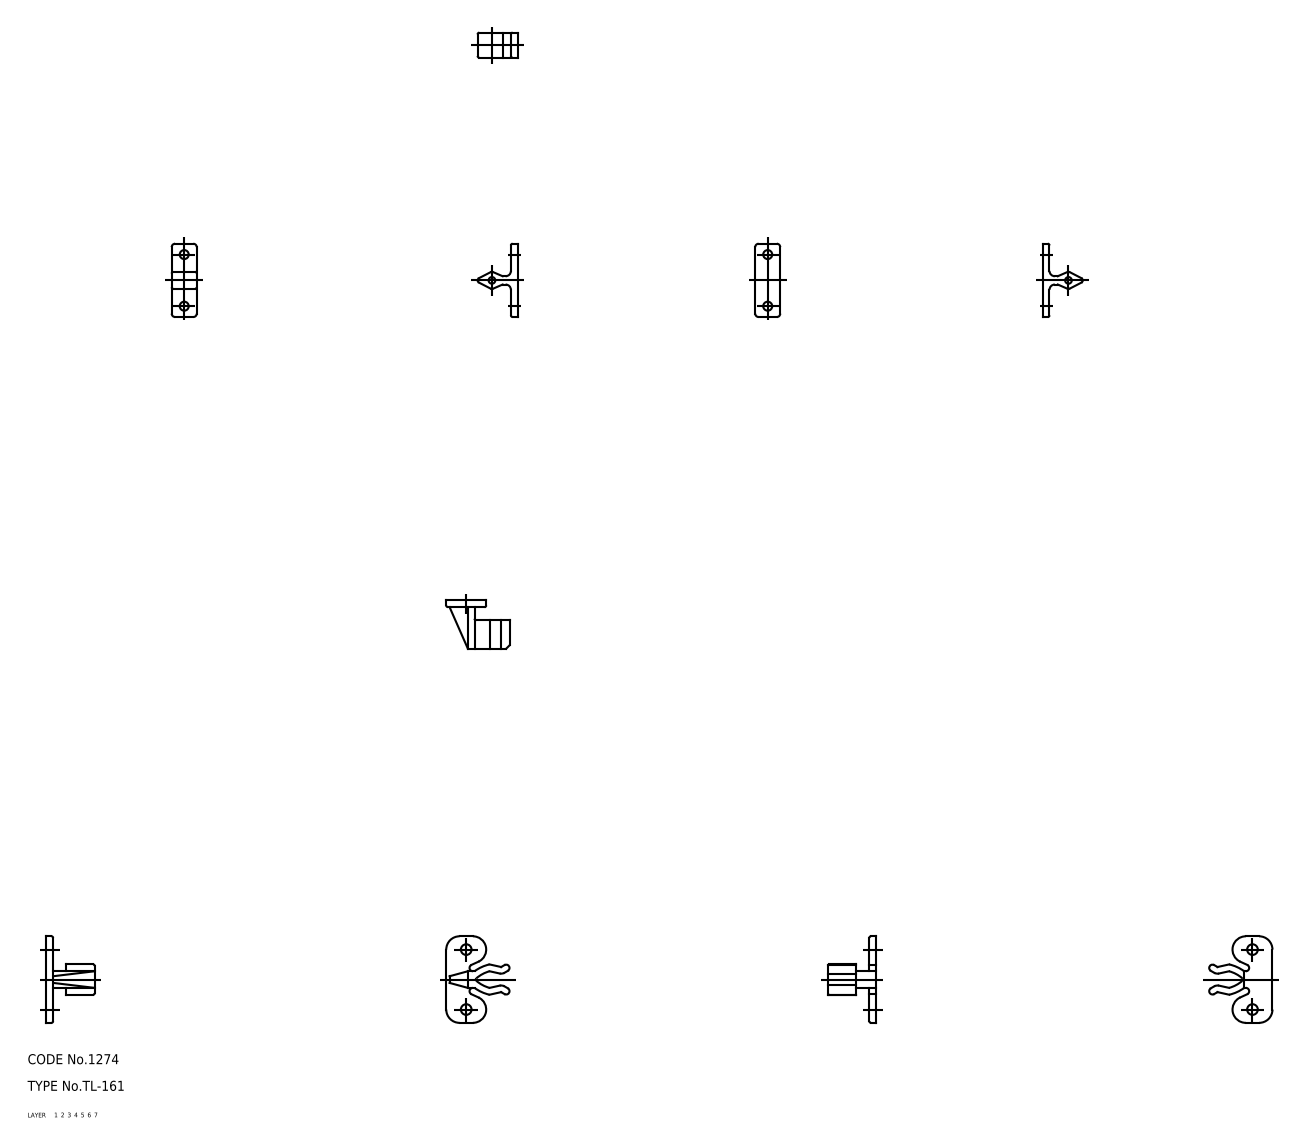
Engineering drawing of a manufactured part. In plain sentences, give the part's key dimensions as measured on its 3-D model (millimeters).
The part is named "keeper; base; TL_161_18357_36". Its 3-D file was written by "CADfix (AUTOMOTIVE_DESIGN)". It is 2 solids with 122 faces: 0 planar, 0 cylindrical and 122 other. Overall it measures 76.78 by 26 by 14.5 millimeters. Its volume is 1 634 cubic millimeters and its surface area 1 986 square millimeters.
